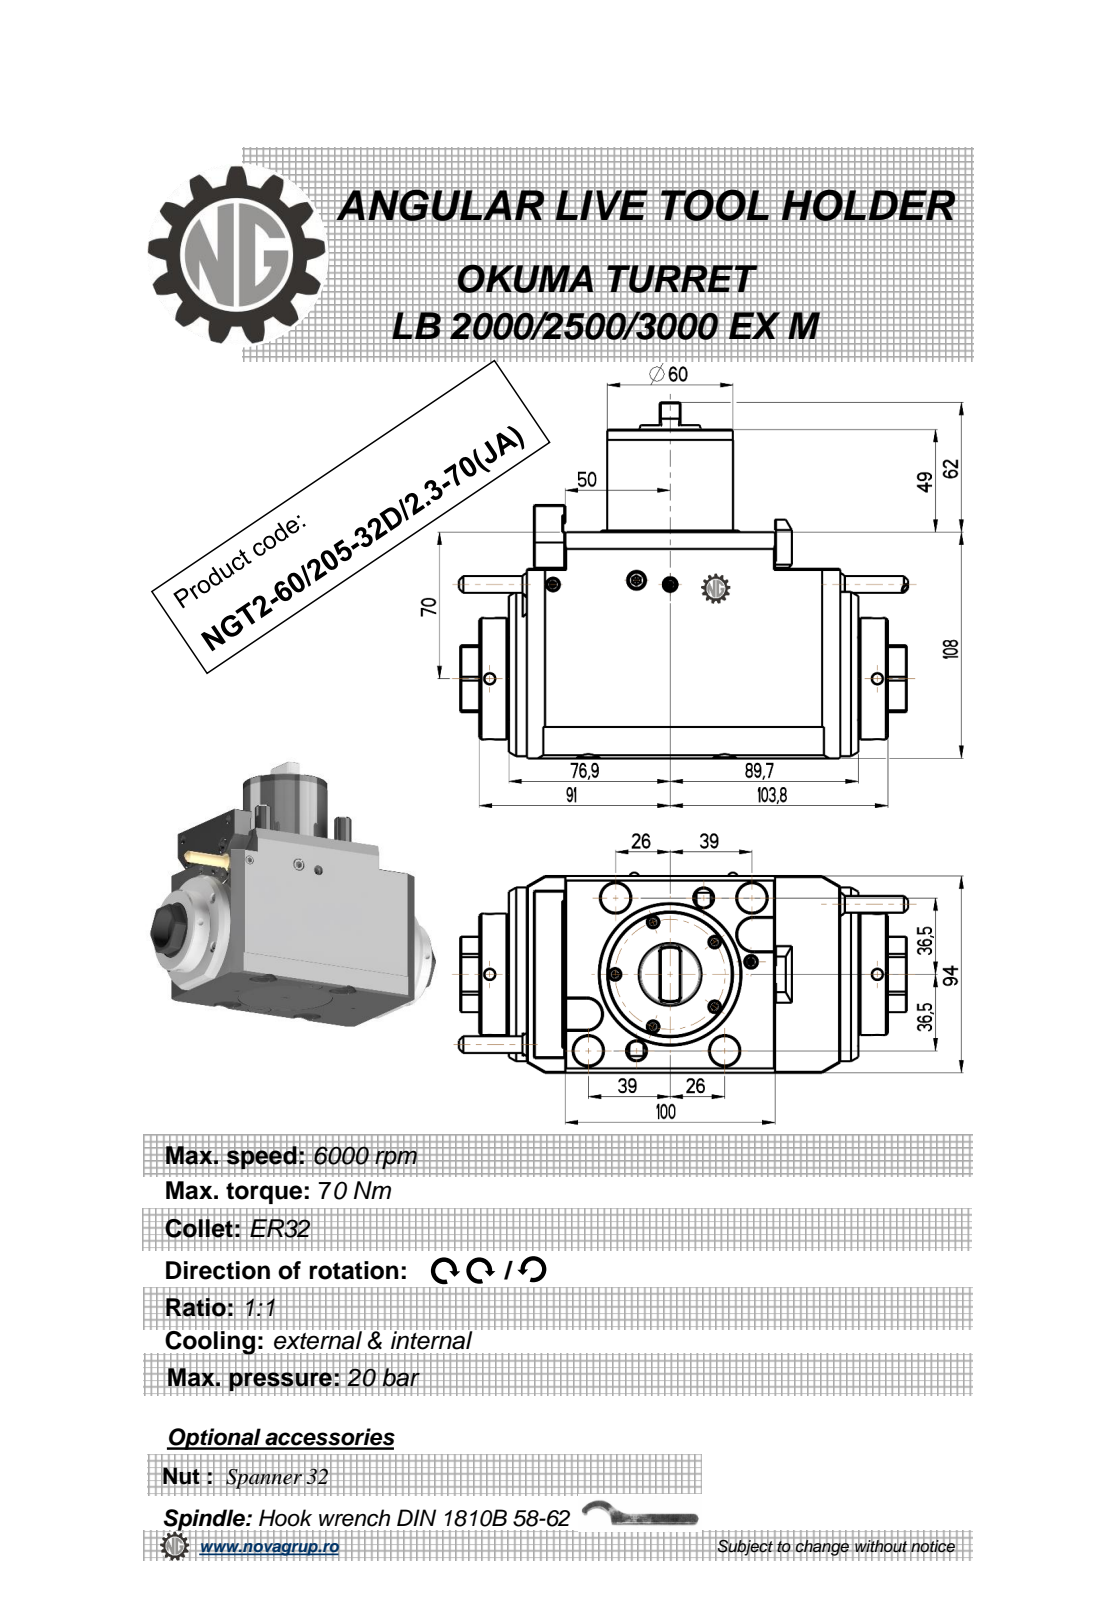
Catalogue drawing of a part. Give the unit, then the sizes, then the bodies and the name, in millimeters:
Units: millimetres
Overall size (bounding box): 214.09 × 170 × 94
Round holes (diameter × count): ⌀5 ×8, ⌀3 ×2, ⌀9 ×2, ⌀27 ×1
Round bosses / shafts (diameter × count): ⌀12 ×4, ⌀6 ×3, ⌀11.2 ×2, ⌀8 ×2, ⌀83 ×1, ⌀60 ×1, ⌀58 ×1, ⌀49 ×1
Partial cylindrical surfaces — rounded edges, fillets, slot ends (radius × count): R0.22 ×12, R0.31 ×10, R0.8 ×6, R7.5 ×1, R8 ×1, R13.25 ×1, R18 ×1, R39.48 ×1
Main face-to-face distances: 94, 108, 158, 90.5, 17.5, 8.6, 14.1, 22.7, 172.1, 180.7
Hole centre spacings: 32.04, 56.1, 72.9, 83.38, 184.8, 64, 67, 78.94
Volume: 1 768 000 mm³ · Surface area: 118 429 mm²
Bodies: 1 solid, 473 faces (199 planar, 125 cylindrical, 149 other)
Part name (STEP PRODUCT): NGT2_60_201_32D_2_3_70_JA
STEP written by: PRO/ENGINEER BY PARAMETRIC TECHNOLOGY CORPORATION, 2010280 (CONFIG_CONTROL_DESIGN)
